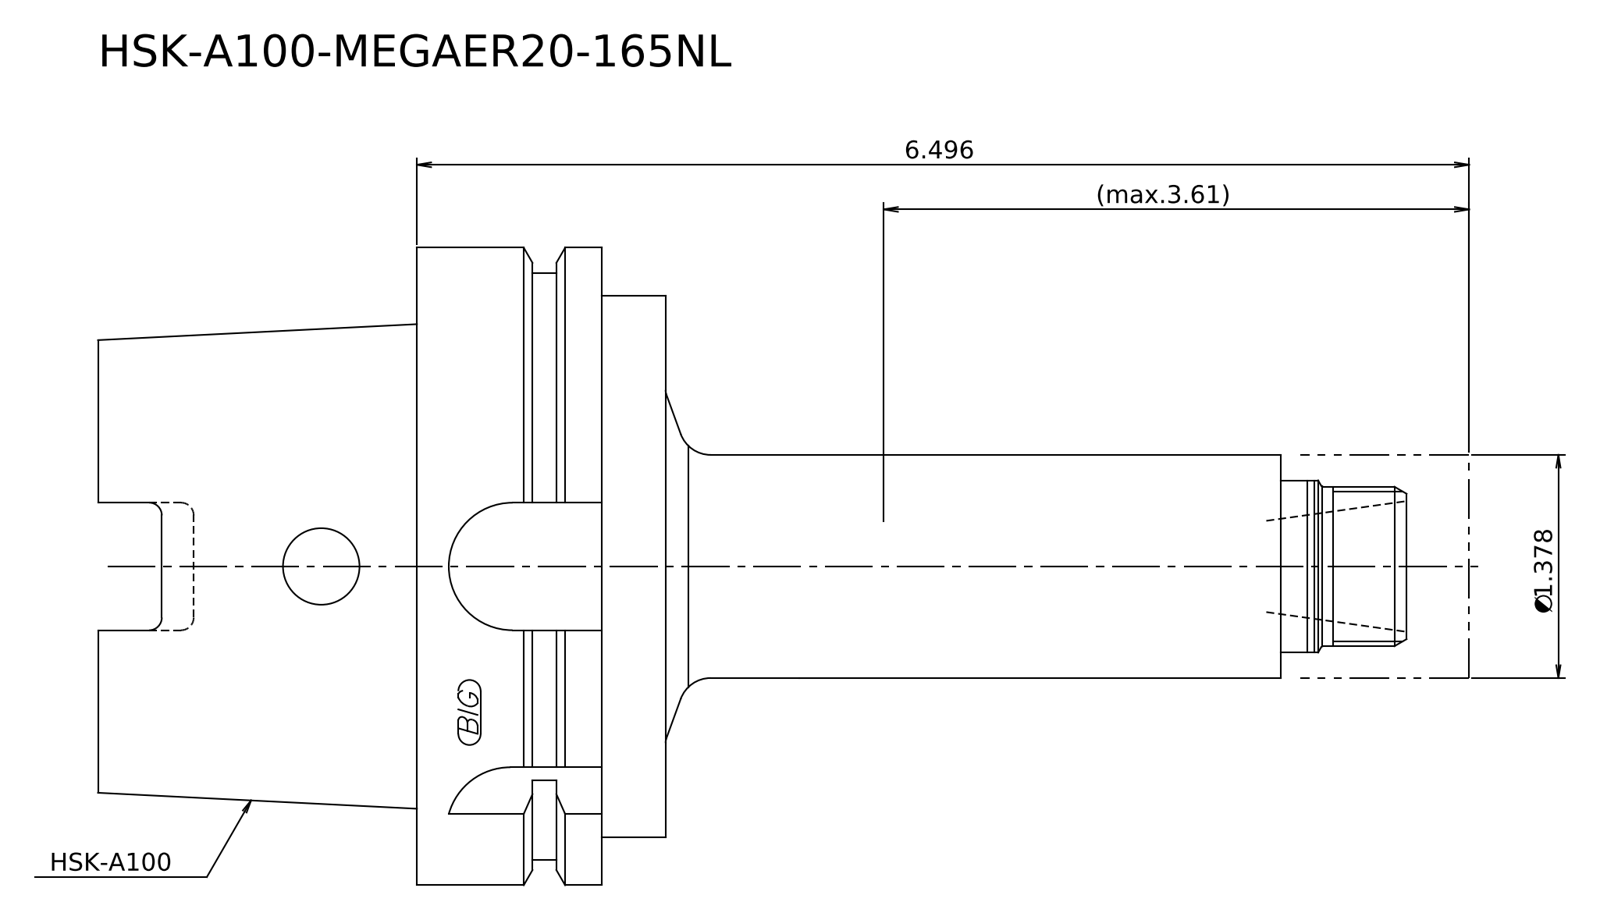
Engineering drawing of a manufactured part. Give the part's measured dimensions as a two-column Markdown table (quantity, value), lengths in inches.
| quantity | value |
| --- | --- |
| STEP written by | Kubotek KeyCreator 2011 V10.0.2 (22737) (automotive_design) |
| units | inches |
| bodies | 2 solids, 24 faces (10 planar, 8 cylindrical, 6 other) |
| overall size | 8.465 × 3.937 × 3.937 |
| volume | 38.1 in³ |
| surface area | 87.77 in² |
| round bosses / shafts (diameter × count) | 3.937 × 1, 3.622 × 1, 3.346 × 1, 1.378 × 1, 1.063 × 1, 0.984 × 1 |
| main face-to-face distances | 1.969, 1.535, 3.504, 0.394, 1.142, 3.11, 3.917, 4.311, 5.453, 7.421 |
